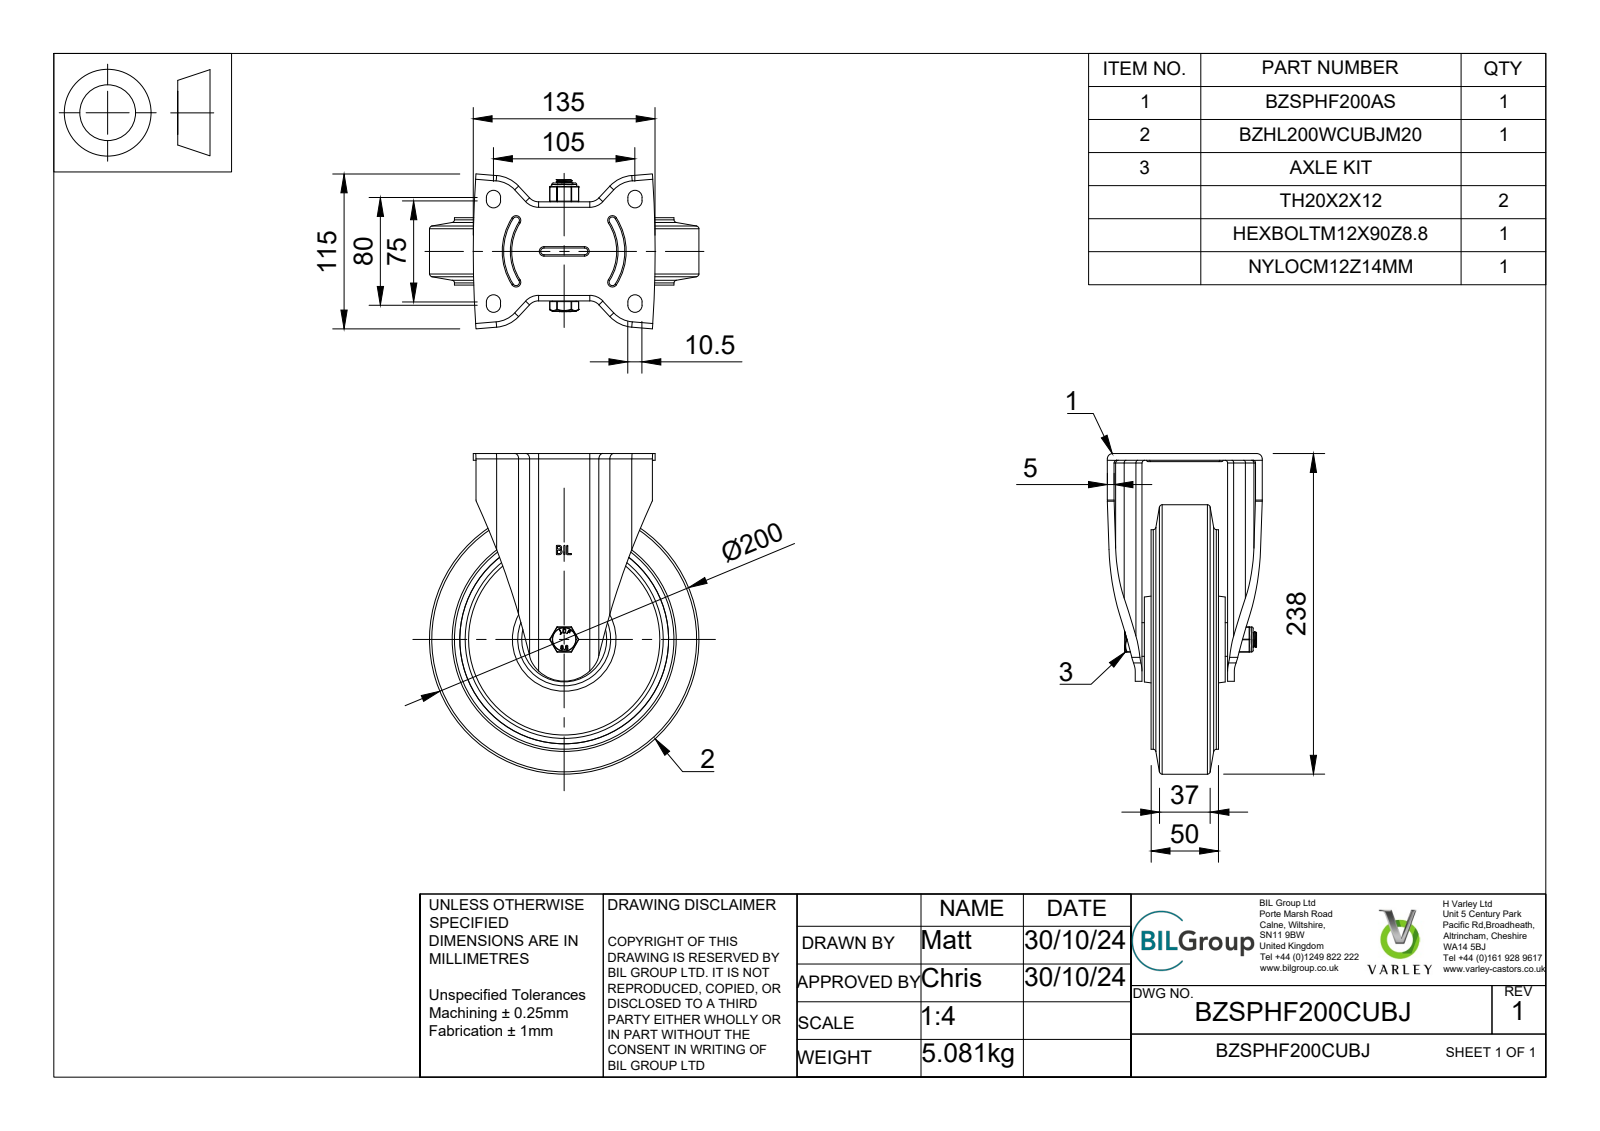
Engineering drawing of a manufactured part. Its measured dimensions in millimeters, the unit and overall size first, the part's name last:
Units: millimetres
Overall size (bounding box): 238 × 200 × 115
Round holes (diameter × count): ⌀12 ×1, ⌀12.2 ×1, ⌀14 ×1, ⌀20 ×1, ⌀28.5 ×1, ⌀30.8 ×1, ⌀37 ×1, ⌀40.3 ×1, ⌀40.5 ×1, ⌀42 ×1, ⌀47 ×1, ⌀147 ×1
Round bosses / shafts (diameter × count): ⌀200 ×1, ⌀163 ×1, ⌀40.8 ×1, ⌀31.3 ×1, ⌀28 ×1, ⌀27 ×1, ⌀25 ×1, ⌀19.8 ×1
Partial cylindrical surfaces — rounded edges, fillets, slot ends (radius × count): R0.5 ×22, R2 ×12, R4 ×10, R5.25 ×8, R0.47 ×4, R0.9 ×4, R1 ×4, R9.21 ×4
Main face-to-face distances: 5, 32.75, 40.75, 61.75, 6.75, 68.5, 27.75, 35.75, 8, 29
Volume: 1 134 000 mm³ · Surface area: 316 053 mm²
Bodies: 35 solids, 1141 faces (437 planar, 245 cylindrical, 459 other)
Part name (STEP PRODUCT): BZSPHF200CUBJ v3; BZSPHF200AS v1; PRESSED STEEL BRACKET; BZHL200WCUBJM20 v1 (+8 more)
STEP written by: Autodesk Translation Framework v13.20.0.188 (AUTOMOTIVE_DESIGN)
